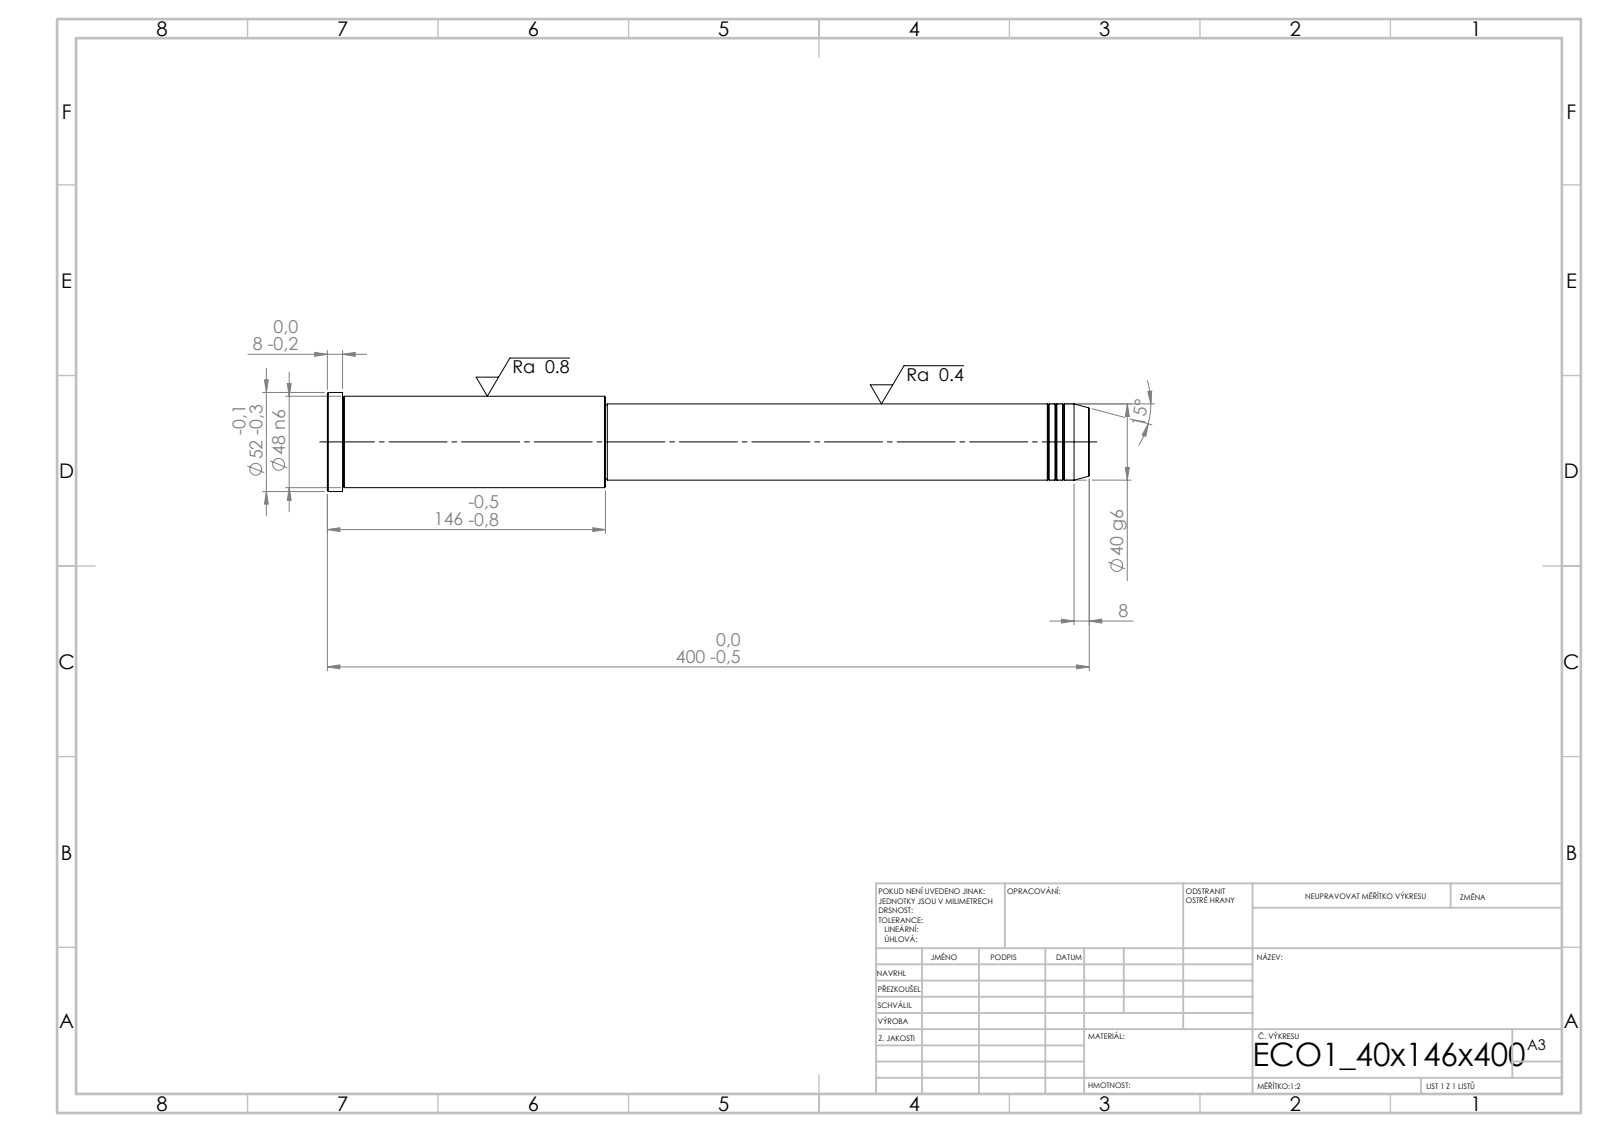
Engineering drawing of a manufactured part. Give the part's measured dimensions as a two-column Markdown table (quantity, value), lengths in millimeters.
| quantity | value |
| --- | --- |
| STEP written by | SolidWorks 2019 (CONFIG_CONTROL_DESIGN) |
| units | millimeters |
| bodies | 1 solid, 43 faces (5 planar, 14 cylindrical, 24 other) |
| overall size | 400 × 52 × 52 |
| volume | 584 546 mm³ |
| surface area | 58 312 mm² |
| round bosses / shafts (diameter × count) | 52 × 1, 48 × 1, 40 × 1, 39 × 1 |
| main face-to-face distances | 400, 254, 146, 392, 138, 8, 253, 1, 139, 147 |
